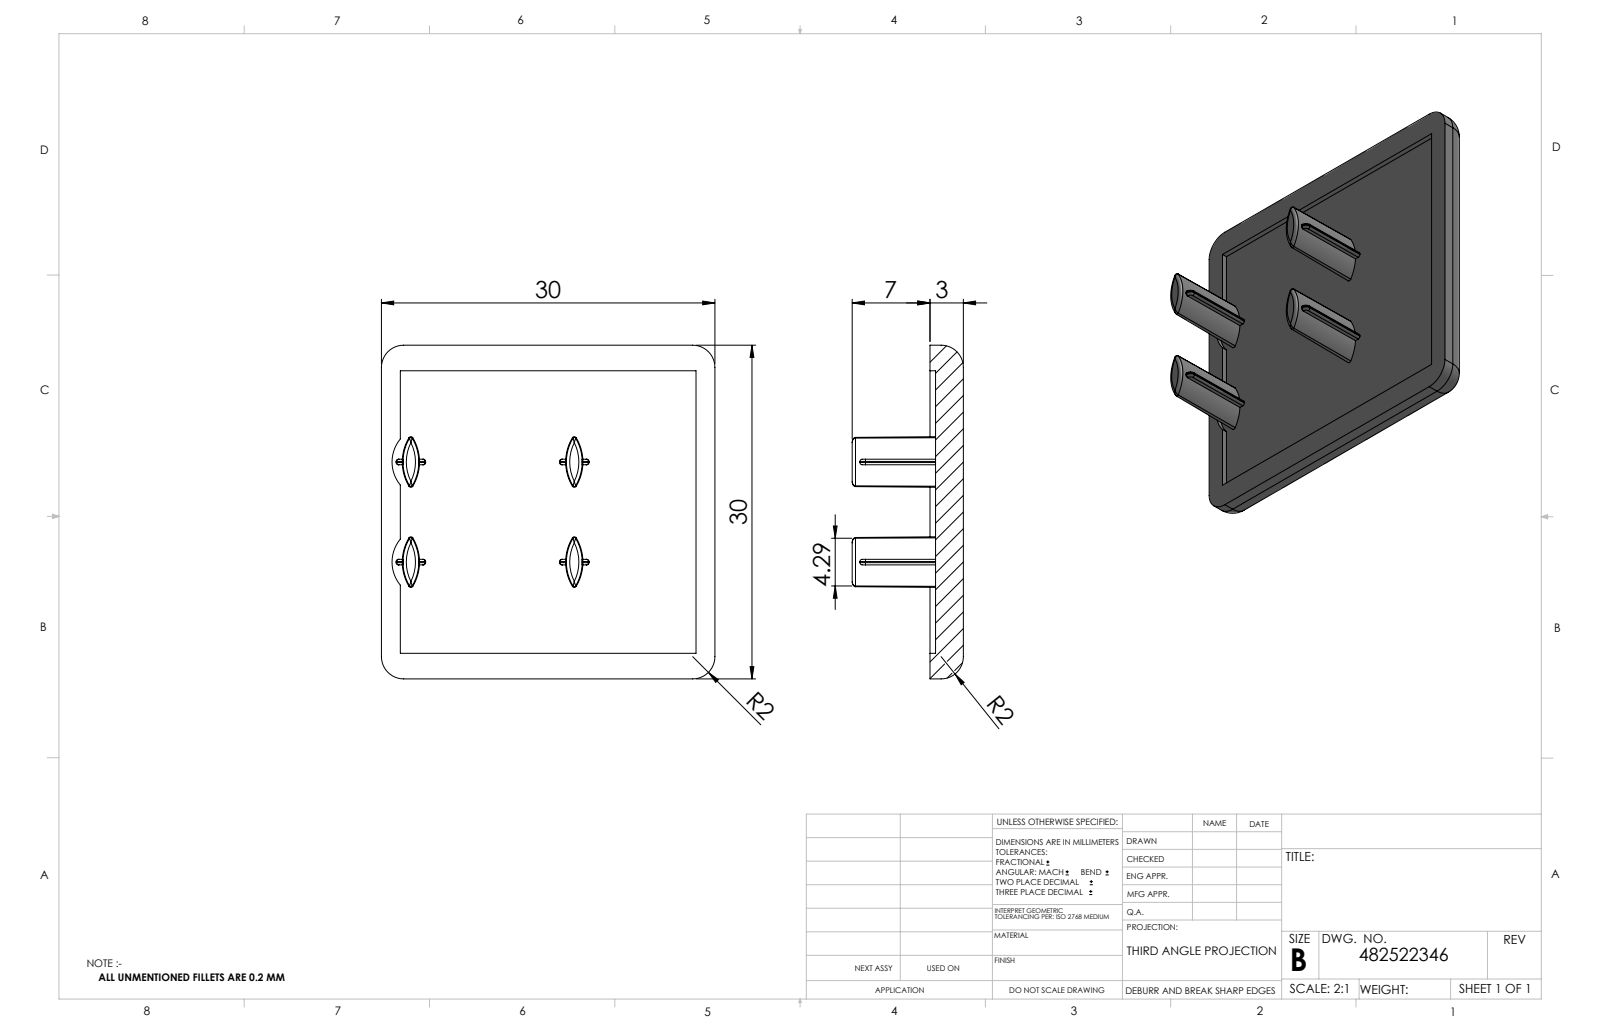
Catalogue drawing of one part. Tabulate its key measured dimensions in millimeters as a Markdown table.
| quantity | value |
| --- | --- |
| part name | 482522346 |
| STEP written by | SolidWorks 2014 (CONFIG_CONTROL_DESIGN) |
| units | millimeters |
| bodies | 1 solid, 160 faces (49 planar, 50 cylindrical, 61 other) |
| overall size | 30 × 30 × 10 |
| volume | 2 409 mm³ |
| surface area | 2 428 mm² |
| partial cylindrical surfaces (radius × count) | 0.2 × 20, 2 × 8, 0.5 × 4, 3.25 × 2 |
| main face-to-face distances | 2.5, 0.5, 3, 30, 2.3, 27.7, 1.7, 28.3, 10.75, 19.25 |
